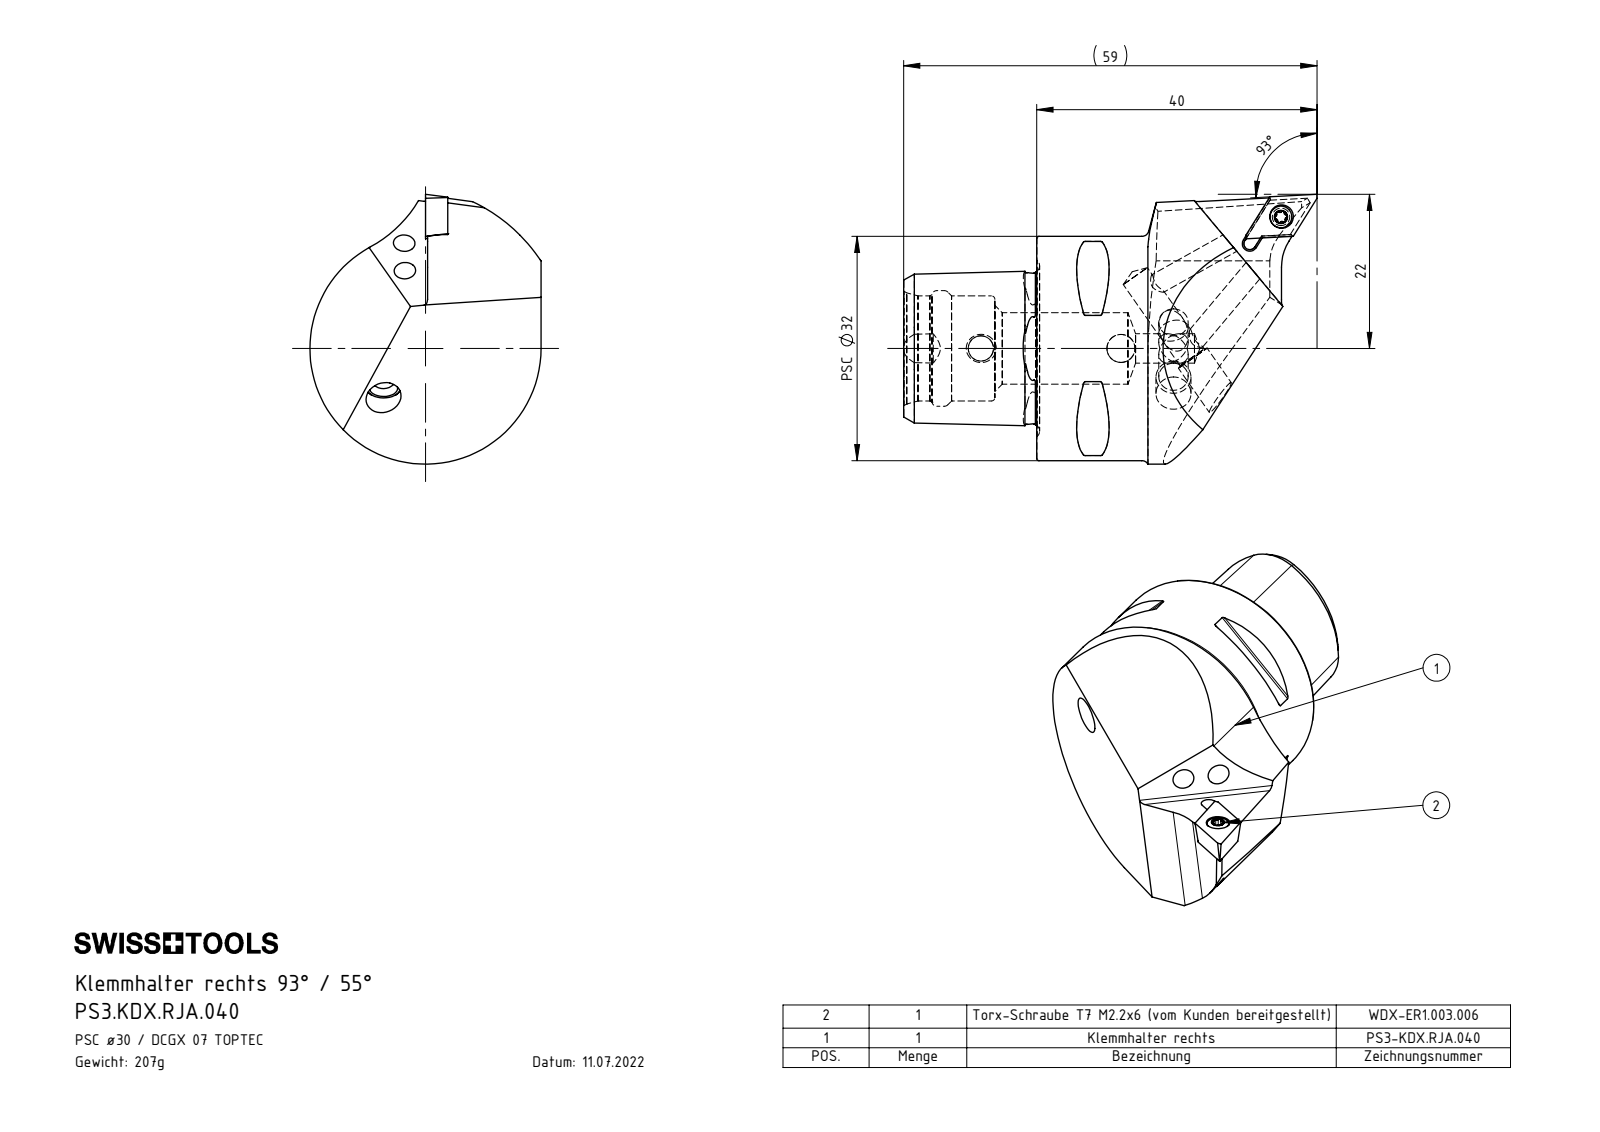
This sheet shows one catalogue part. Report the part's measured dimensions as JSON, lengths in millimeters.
{"part_name": "KVT_MB_600_050; PS3-KDX.RJA.040; DCGX 07 TOPDEC; WDX-ER1.003.006_A (+1 more)", "step_written_by": "SolidWorks 2017 (AUTOMOTIVE_DESIGN)", "units": "millimeters", "bodies": {"solids": 7, "faces": 294, "planar": 49, "cylindrical": 88, "other": 157}, "overall_size": [59, 38.5, 33], "volume_mm3": 26263, "surface_area_mm2": 9015, "round_holes": [[4, 3], [4.2, 3], [3, 2], [5, 2], [1.75, 1], [2.5, 1], [3.35, 1], [3.6, 1], [10.2, 1], [15, 1], [16.5, 1]], "round_bosses_or_shafts": [[5, 2], [32, 1], [3.1, 1], [2.2, 1]], "partial_cylinders_radius": [[0.3, 8], [0.21, 6], [0.26, 6], [0.5, 1], [0.85, 1], [3, 1], [7, 1], [16.5, 1]], "face_to_face_distances": [19, 12.01, 28.3, 16.2, 13.32, 2.88, 13, 6, 16.5, 3.18], "hole_center_spacings": [20, 29.58, 29.69, 46.79, 46.9]}
